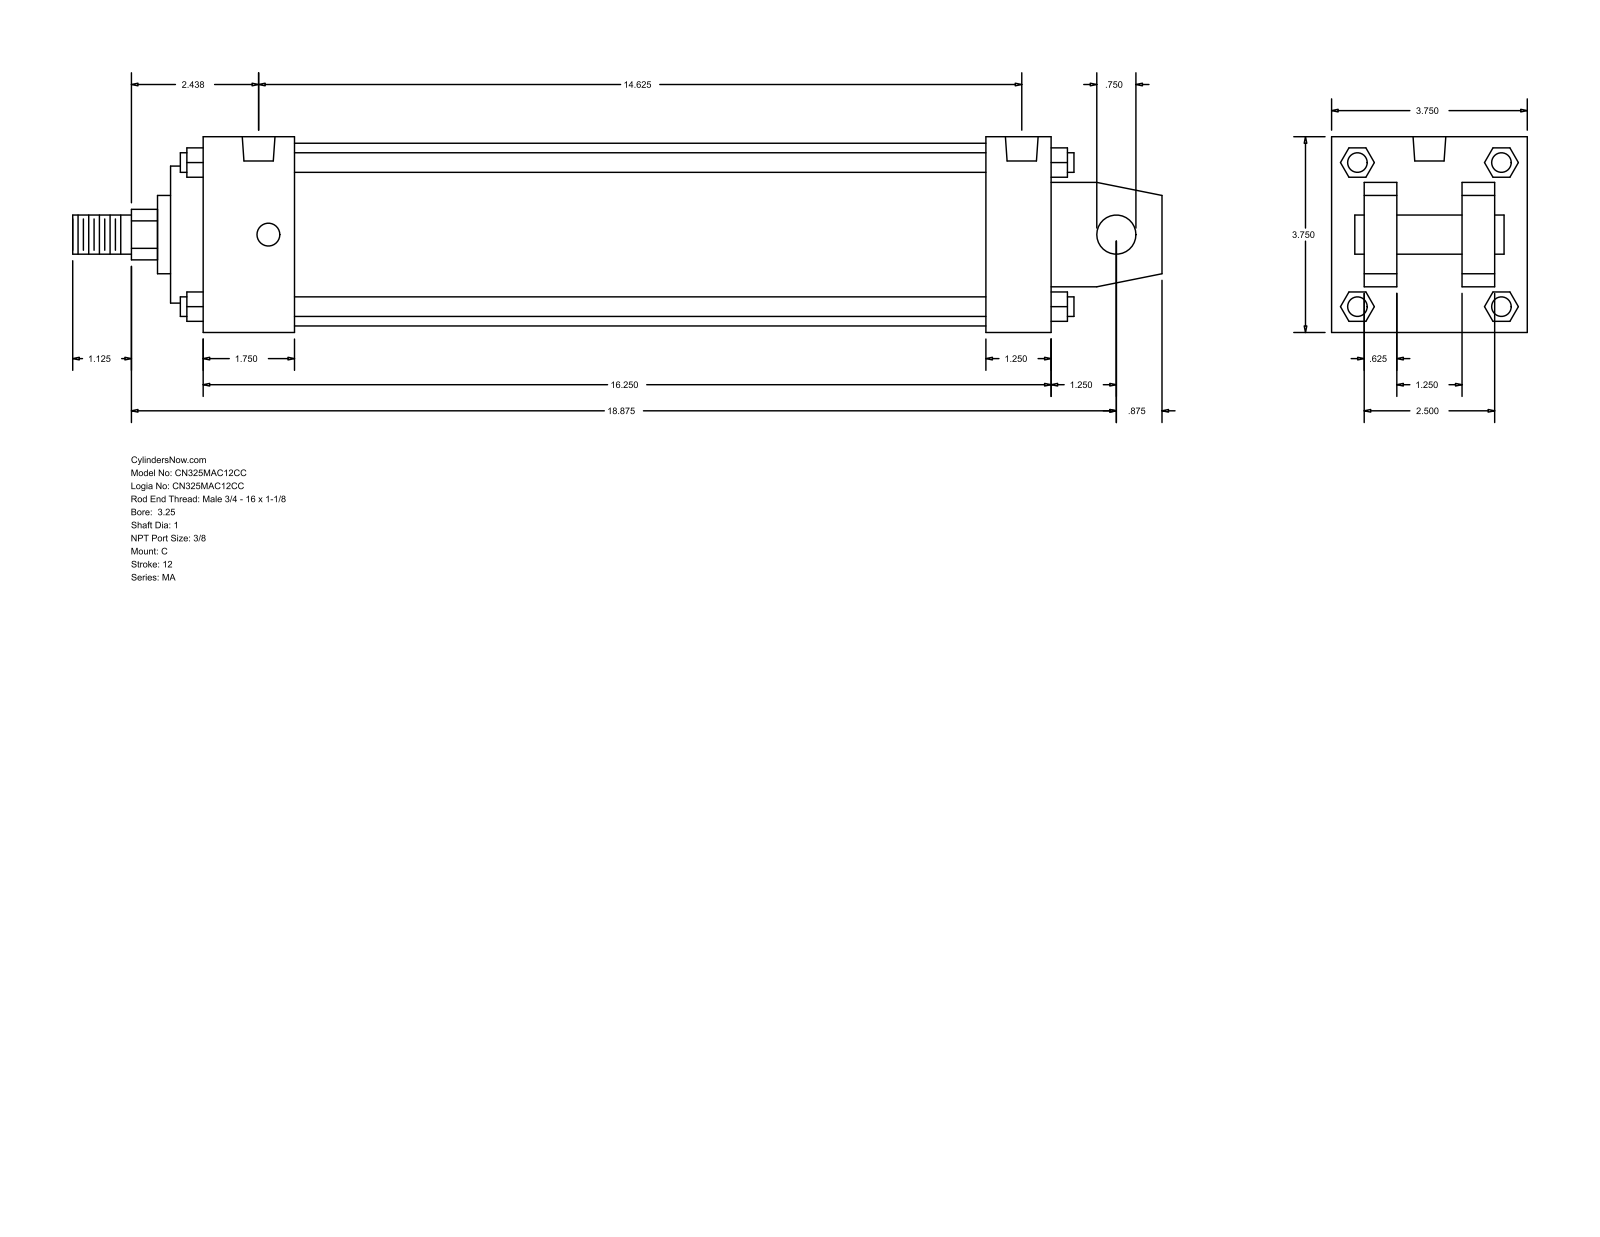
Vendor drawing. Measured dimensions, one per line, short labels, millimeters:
name: MA_C__0325_1
written by: GSSL Pune (CONFIG_CONTROL_DESIGN)
unit: mm
bodies: 0 solids, 141 faces (109 planar, 32 cylindrical, 0 other)
size: 530.23 × 95.25 × 95.25
holes: 4× ⌀11.11, 2× ⌀15.93
bosses: 4× ⌀9.53, 2× ⌀19.05, 1× ⌀88.9, 1× ⌀66.67, 1× ⌀38.1, 1× ⌀25.4
rounds: 1× R12.29
face distances: 95.24, 15.87, 63.5, 412.76, 31.74, 79.37, 47.63, 381.01, 31.75, 44.46
hole spacings: 361.95, 4.76, 4.77, 366.71, 366.72, 371.48
